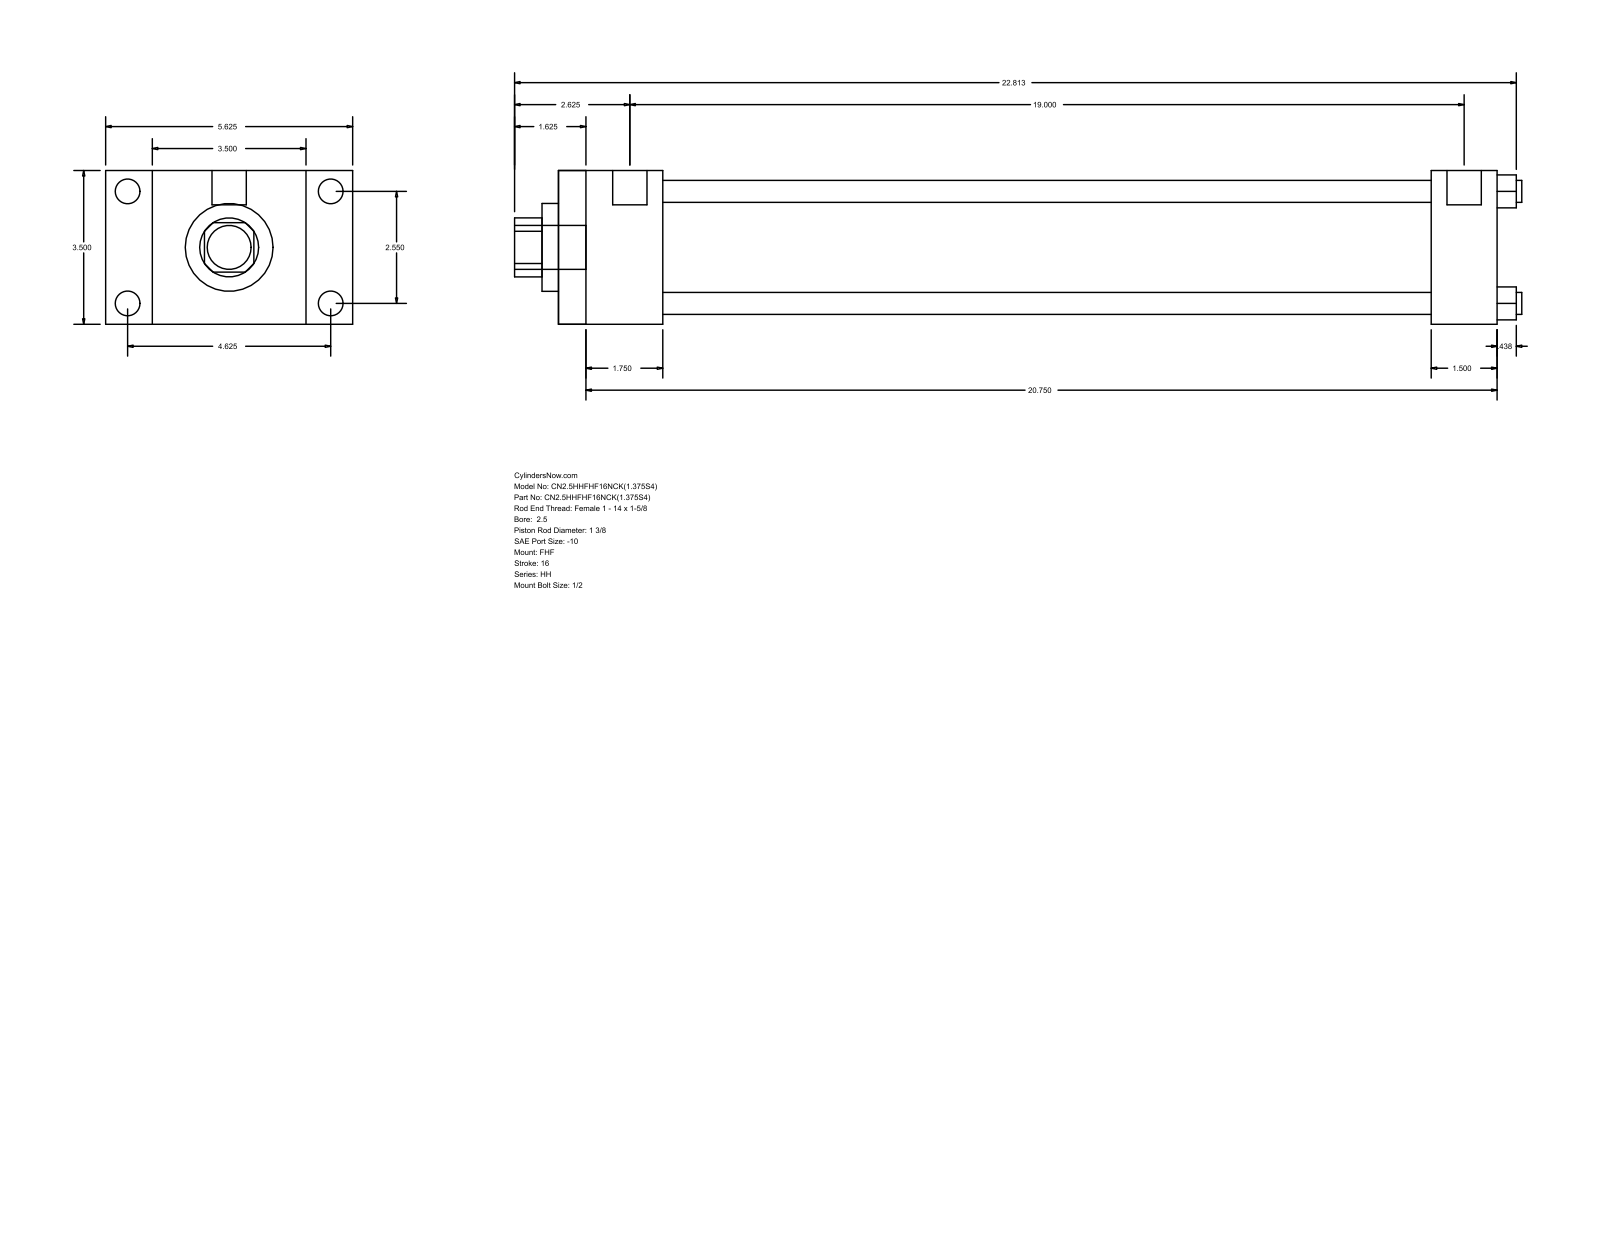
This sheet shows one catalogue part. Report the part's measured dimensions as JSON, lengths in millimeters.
{"part_name": "HH_FHF__0250_1.375", "step_written_by": "GSSL Pune (CONFIG_CONTROL_DESIGN)", "units": "millimeters", "bodies": {"solids": 0, "faces": 88, "planar": 60, "cylindrical": 28, "other": 0}, "overall_size": [582.61, 142.88, 88.9], "round_holes": [[12.7, 4], [34.92, 1], [50.8, 1], [73.03, 1]], "round_bosses_or_shafts": [[14.3, 4], [5.56, 4], [19.84, 2], [25.4, 1]], "partial_cylinders_radius": [[17.06, 1]], "face_to_face_distances": [88.9, 60.32, 26.99, 115.89, 542.93, 482.61, 142.88, 504.83, 444.51, 38.1], "hole_center_spacings": [45.79, 64.76, 91.58]}
